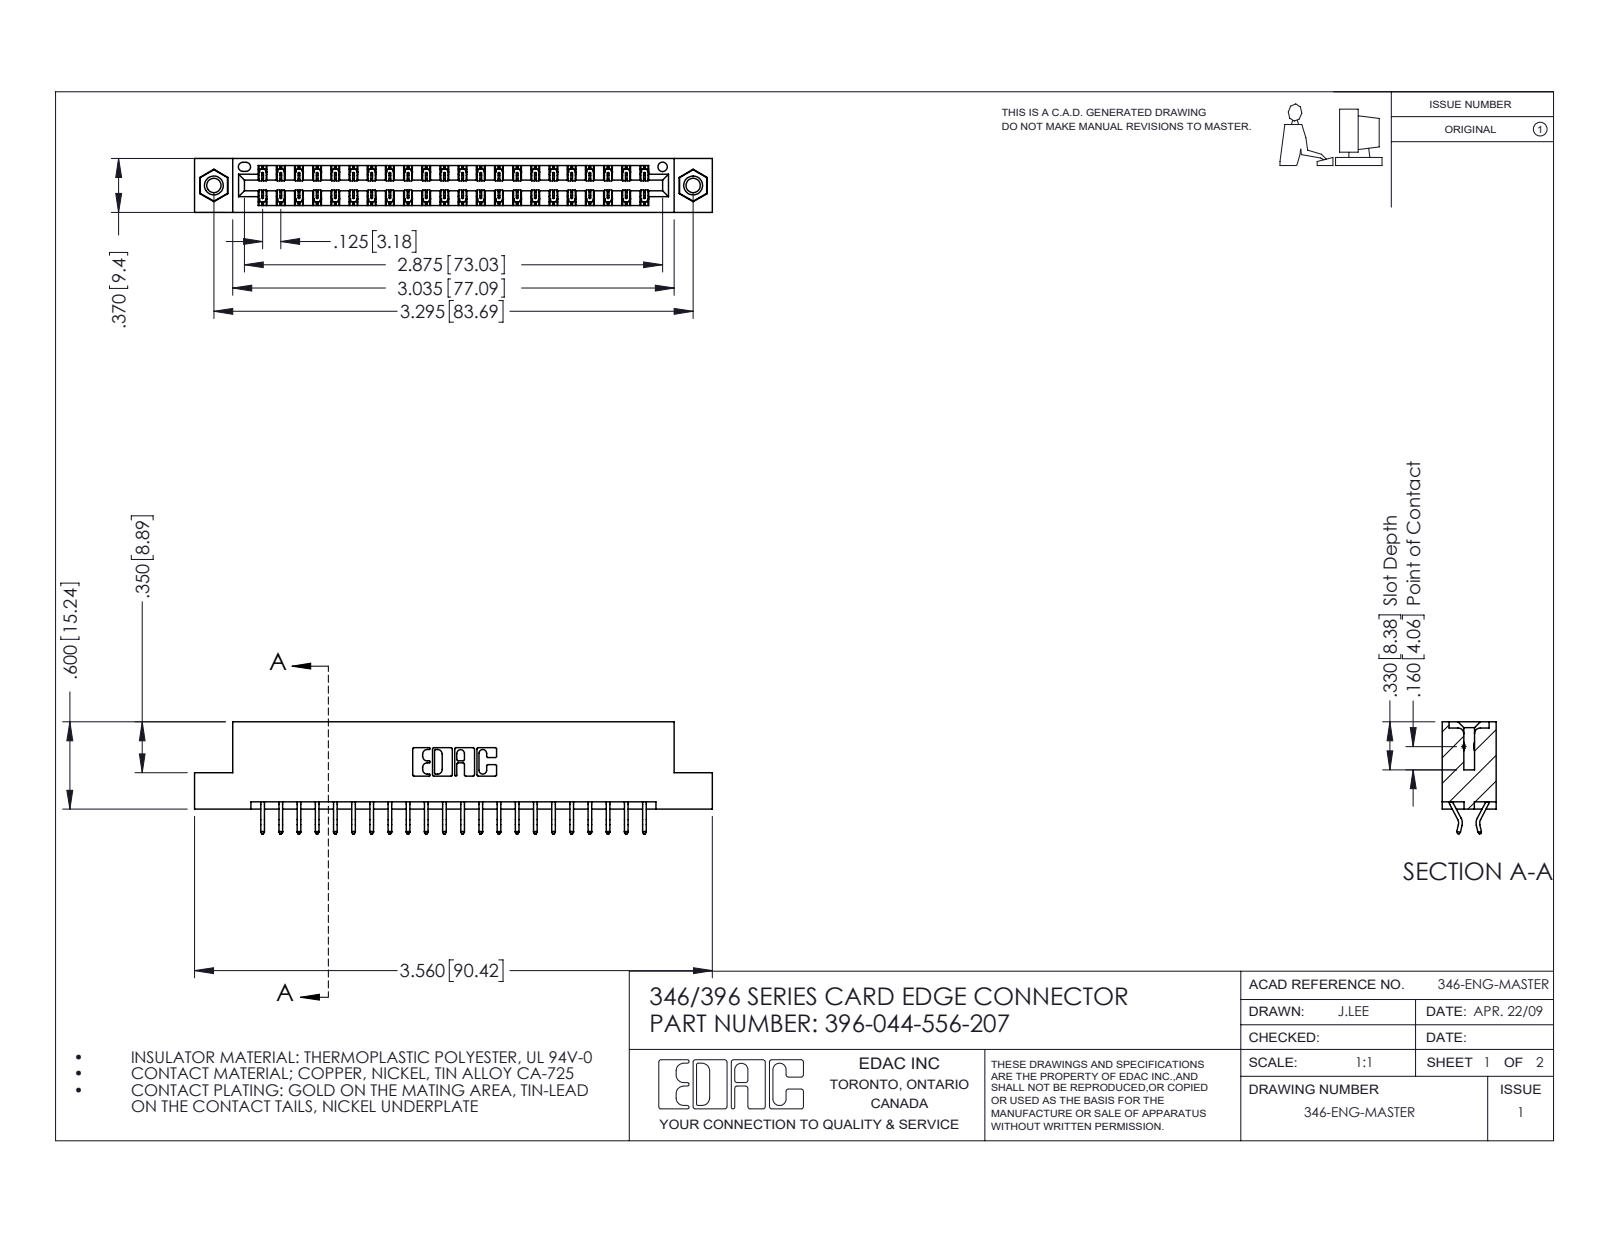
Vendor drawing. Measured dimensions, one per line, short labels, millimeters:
name: 396-044-556-207; 345-292-001_556 Tail; 346 Part_Flush Mounting Lugs - 0.156 Dia-TI; 345-250-001_345-250-005-103
written by: SolidWorks 2016 (CONFIG_CONTROL_DESIGN)
unit: mm
bodies: 47 solids, 2734 faces (1824 planar, 894 cylindrical, 16 other)
size: 90.4 × 19.6 × 9.4
volume: 8 650 mm³; area: 11 560 mm²
holes: 2× ⌀2.5, 2× ⌀3.2, 2× ⌀4, 1× ⌀1.6
bosses: 2× ⌀3.9
rounds: 66× R0.2, 22× R0.3, 6× R0.2, 6× R0.8, 3× R0.7, 2× R0.3, 2× R0.4, 2× R0.6
face distances: 1.2, 8.2, 9.4, 6.4, 0.6, 1.8, 7.6, 7, 3.8, 5.6
hole spacings: 6.2, 78.4, 83.7
